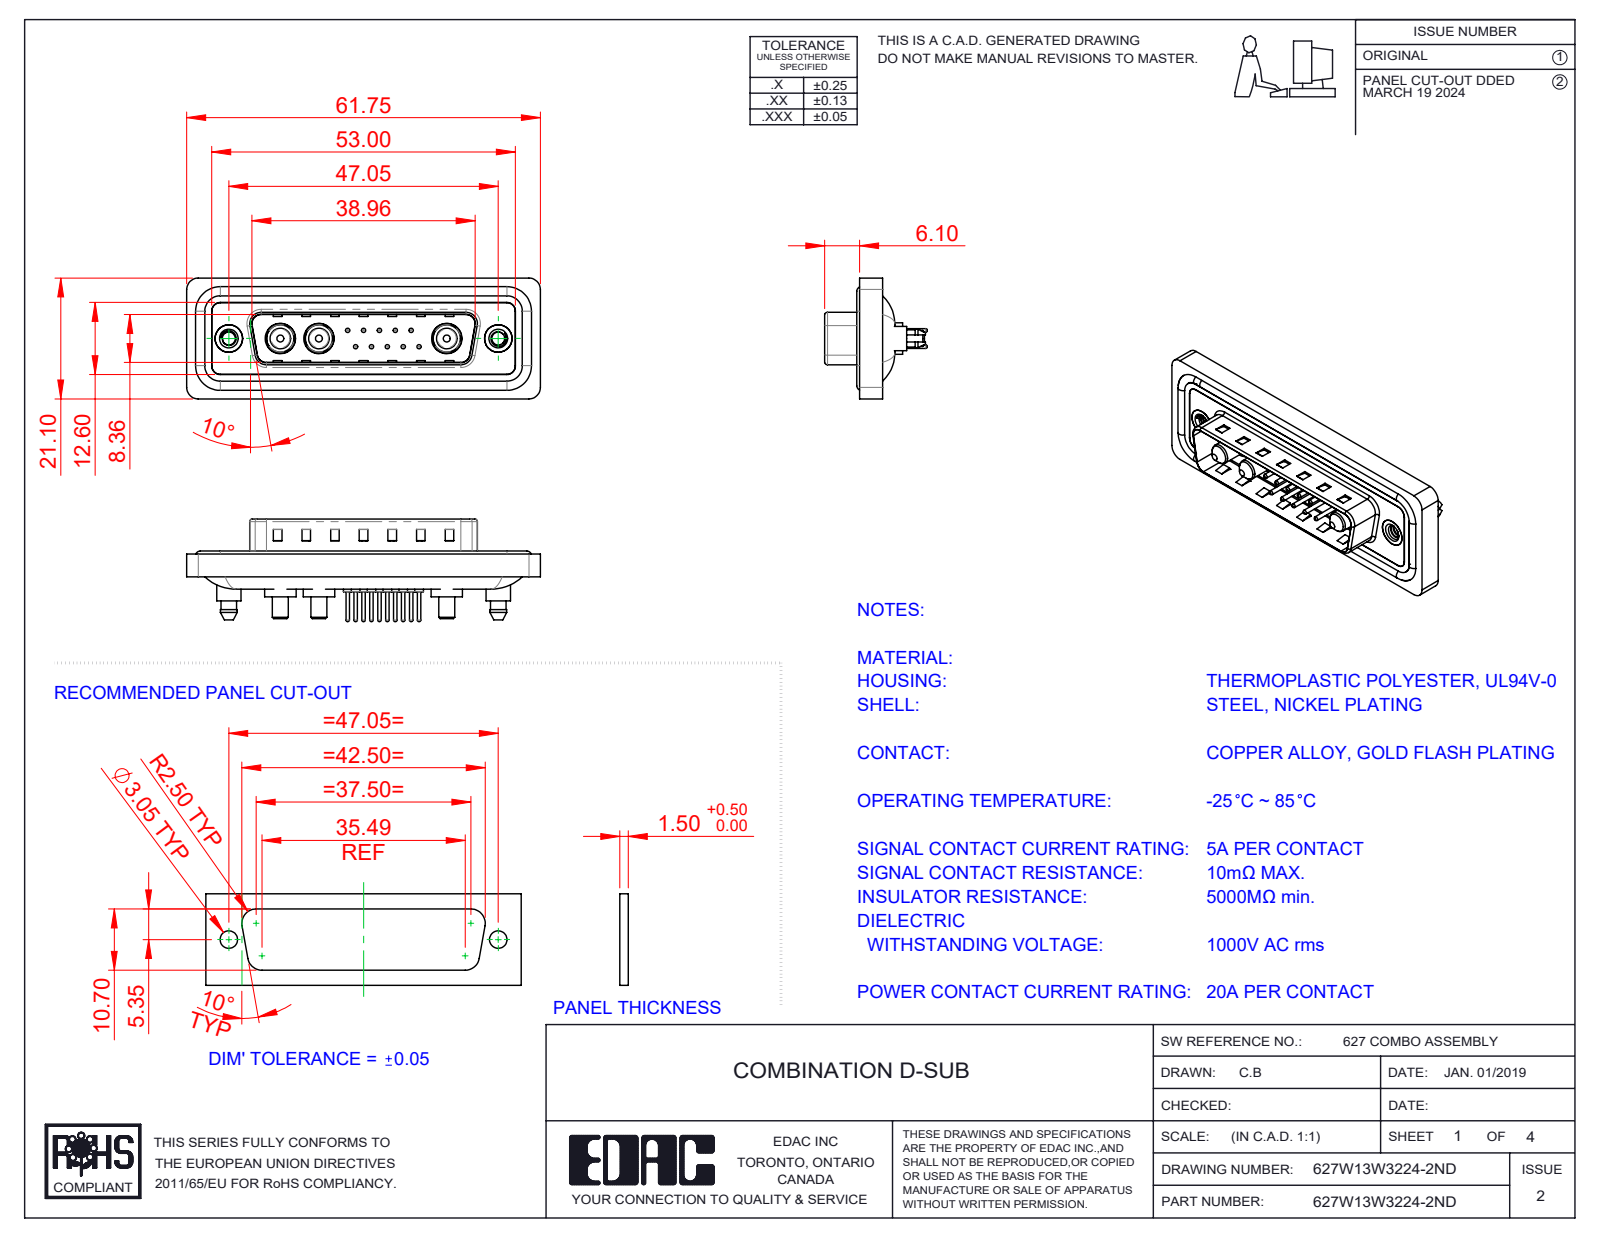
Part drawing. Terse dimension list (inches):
name: Power Pin_20A S; 627Combo Threaded Boardlock_5; 627Combo Shell Rear_25 Contacts; 627Combo Threaded Boardlock_D (+6 more)
written by: SolidWorks 2023 (CONFIG_CONTROL_DESIGN)
unit: in
bodies: 23 solids, 1028 faces (325 planar, 425 cylindrical, 278 other)
size: 2.431 × 0.831 × 0.705
volume: 0.456 in³; area: 18.93 in²
holes: 10× ⌀0.03, 10× ⌀0.063, 10× ⌀0.079, 3× ⌀0.191, 3× ⌀0.209, 2× ⌀0.089, 2× ⌀0.157, 2× ⌀0.189, 2× ⌀0.197
bosses: 10× ⌀0.059, 10× ⌀0.024, 4× ⌀0.063, 3× ⌀0.217, 3× ⌀0.205, 3× ⌀0.187, 3× ⌀0.148, 3× ⌀0.142
rounds: 24× R0.059, 18× R0.079, 10× R0.063, 8× R0.02, 4× R0.01, 4× R0.024, 4× R0.026, 4× R0.035
face distances: 0.016, 0.059, 0.043, 0.063, 0.02, 0.122, 0.114, 0.032, 0.377, 0.161
hole spacings: 0.124, 0.109, 0.198, 0.218, 0.295, 0.198, 0.327, 0.398
